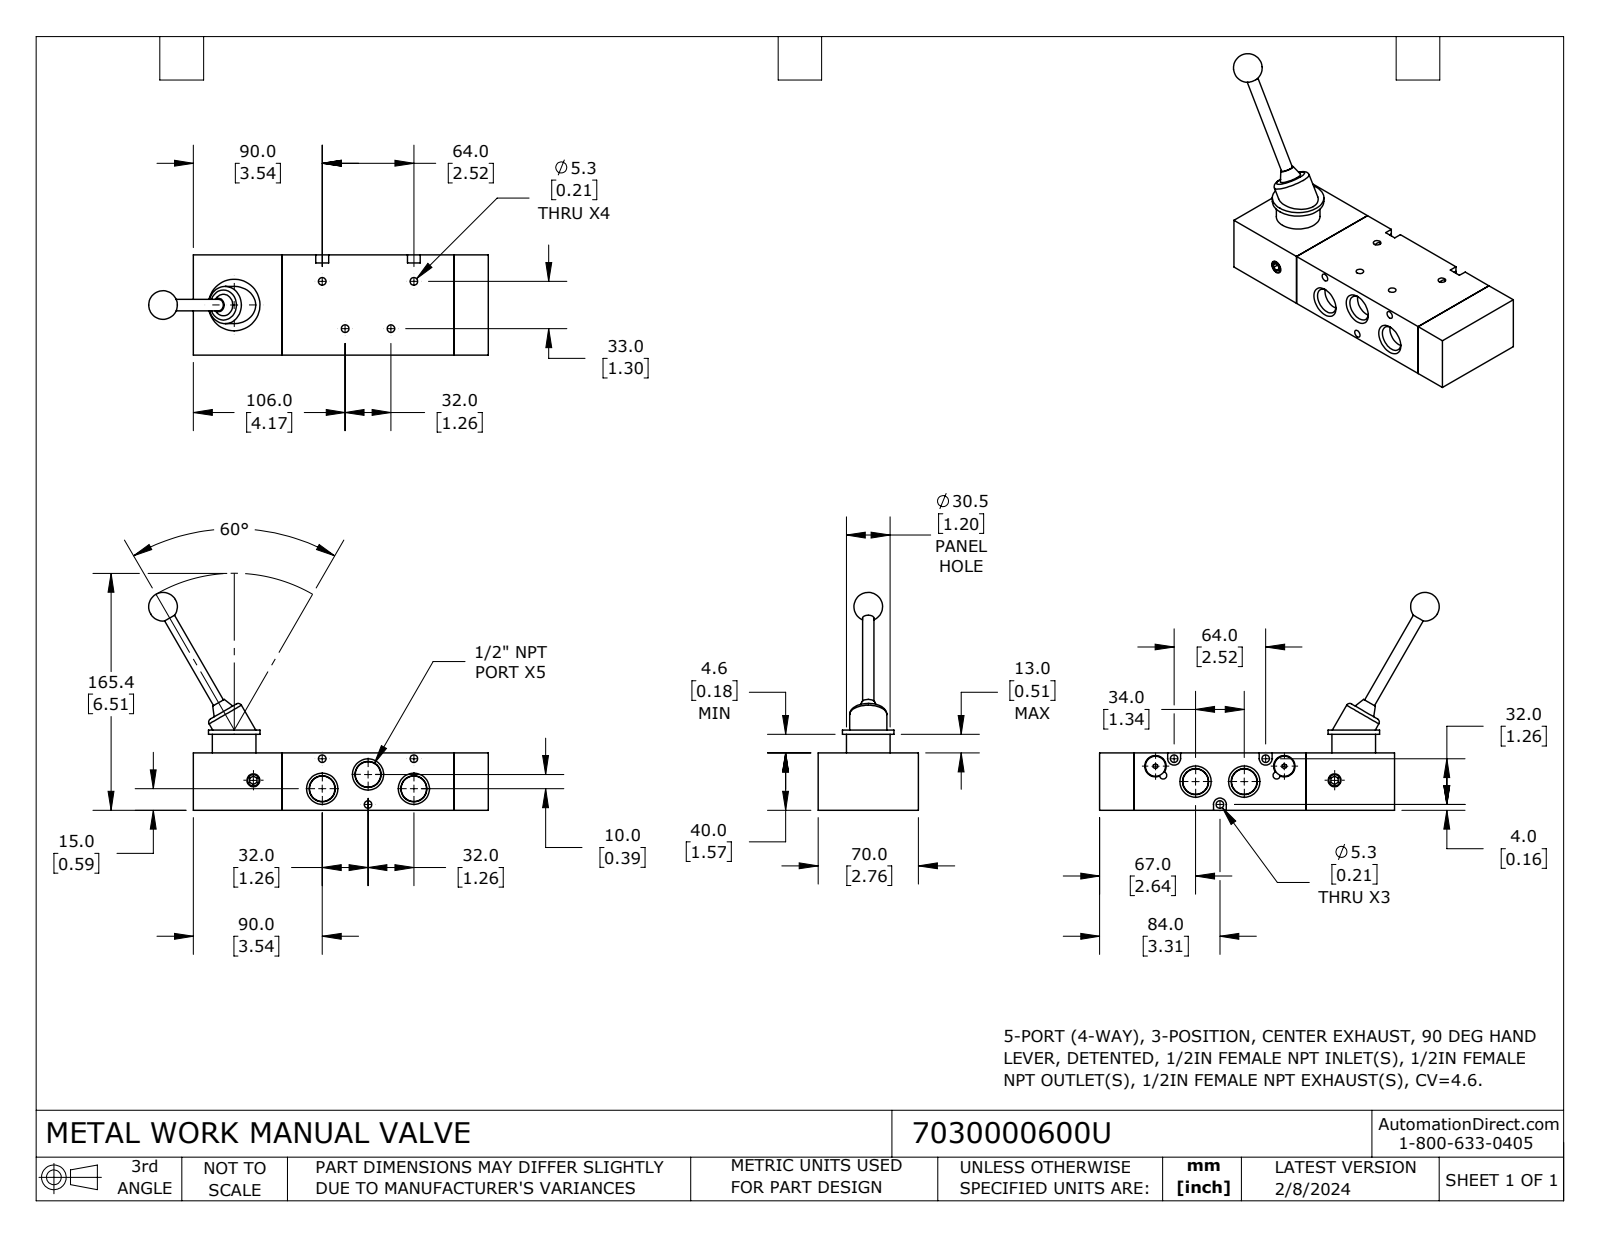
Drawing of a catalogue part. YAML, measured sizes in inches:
part_name: "7030000600U"
step_written_by: "SolidWorks 2023 (CONFIG_CONTROL_DESIGN)"
units: inches
bodies: {solids: 3, faces: 155, planar: 72, cylindrical: 57, other: 26}
overall_size: [9.339, 5.988, 2.756]
volume: 35.65
surface_area: 120.8
round_holes:
  - {diameter: 0.209, count: 7}
  - {diameter: 0.587, count: 2}
  - {diameter: 0.354, count: 1}
round_bosses_or_shafts:
  - {diameter: 0.551, count: 2}
  - {diameter: 1.417, count: 1}
  - {diameter: 1.201, count: 1}
  - {diameter: 1.024, count: 1}
  - {diameter: 0.315, count: 1}
  - {diameter: 0.313, count: 1}
partial_cylinders:
  - {radius: 0.177, count: 3}
  - {radius: 0.098, count: 2}
face_to_face_distances: [1.575, 2.756, 4.724, 0.945, 5.669, 8.11, 7.165, 2.441, 0.354, 2.402]
hole_center_spacings: [0.552, 1.444, 1.781, 2.061, 2.293, 2.52, 3.039, 1.26]
